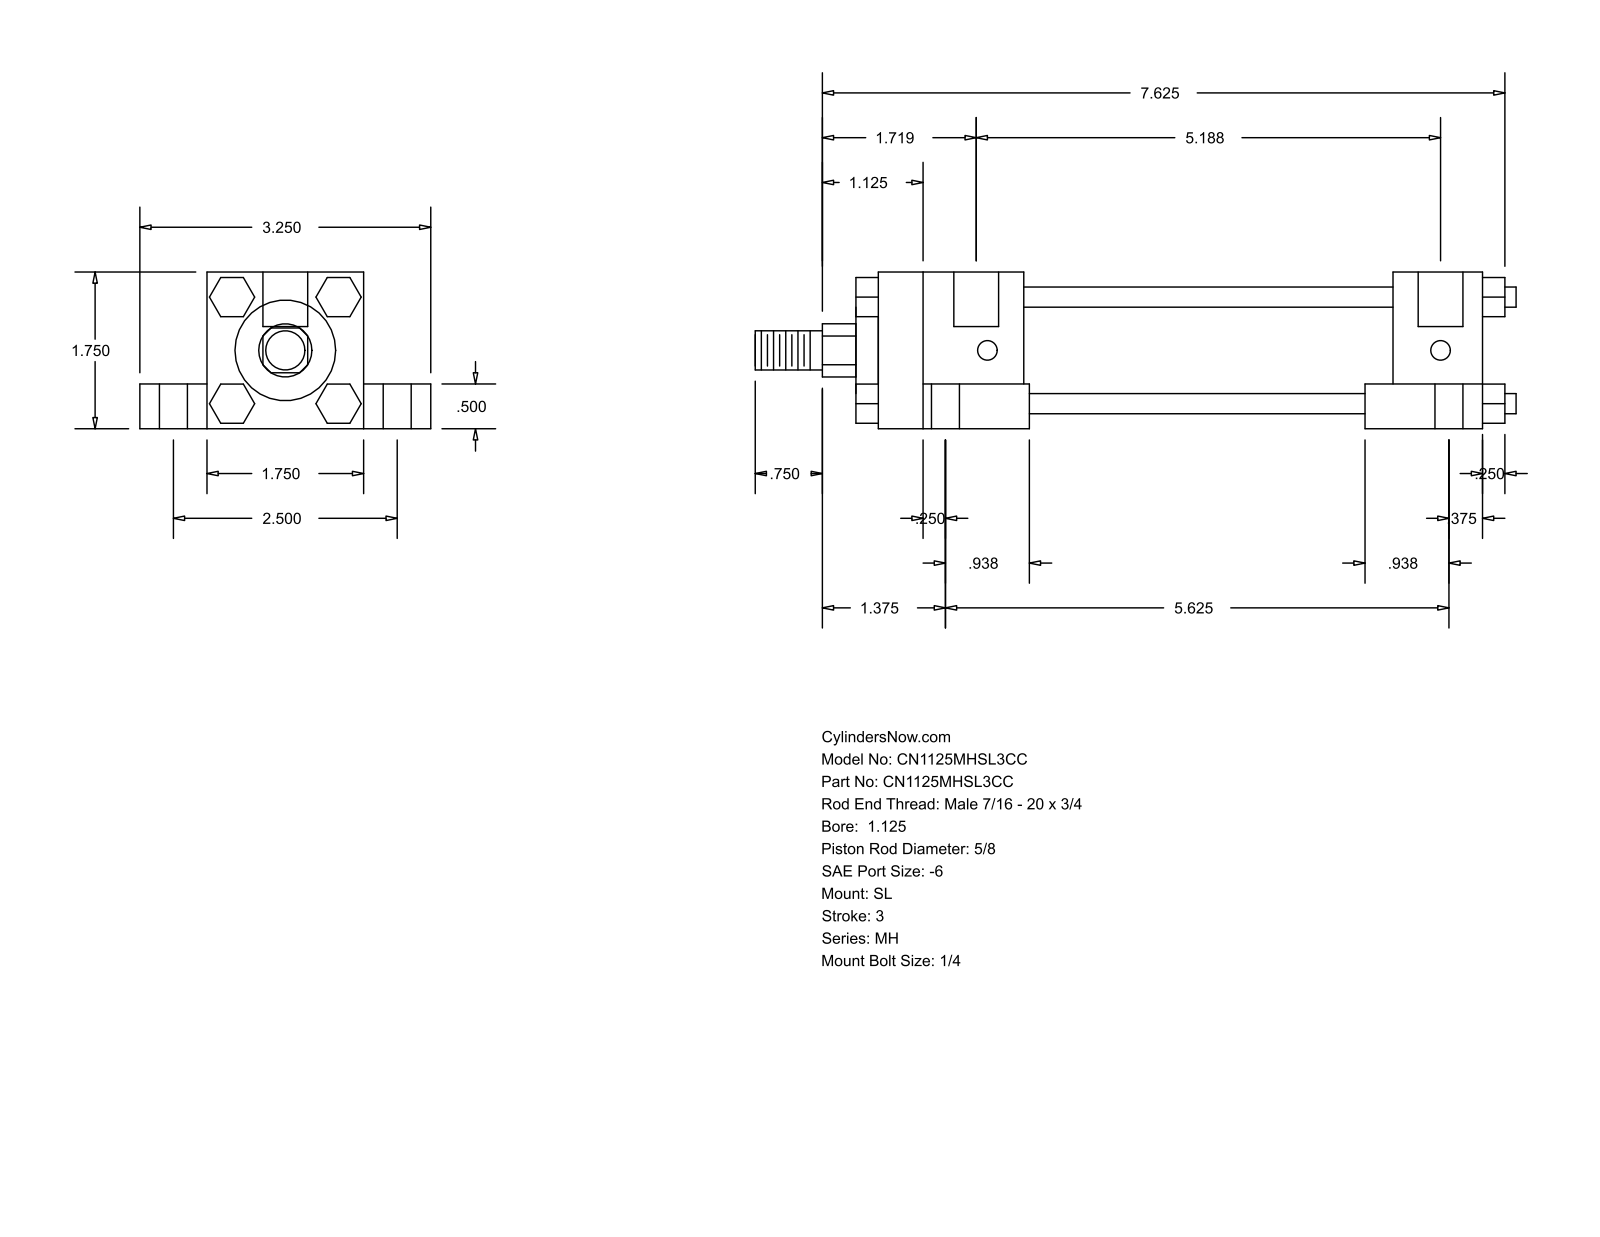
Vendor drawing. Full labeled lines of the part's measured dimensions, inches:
Part name (STEP PRODUCT): MH_SL__0112_0.625
STEP written by: GSSL Pune (CONFIG_CONTROL_DESIGN)
Units: inches
Bodies: 0 solids, 150 faces (114 planar, 36 cylindrical, 0 other)
Overall size (bounding box): 8.5 × 3.25 × 1.75
Round holes (diameter × count): ⌀0.219 ×4, ⌀0.313 ×4, ⌀0.563 ×4, ⌀0.5 ×2
Round bosses / shafts (diameter × count): ⌀0.225 ×4, ⌀1.375 ×1, ⌀1.125 ×1, ⌀0.625 ×1, ⌀0.437 ×1
Partial cylindrical surfaces — rounded edges, fillets, slot ends (radius × count): R0.297 ×1
Main face-to-face distances: 1.75, 0.75, 0.5, 1.25, 2.5, 0.437, 1.875, 4.125, 5.125, 1
Hole centre spacings: 1.254, 1.269, 1.296, 2.5, 5.063, 5.306, 5.427, 5.5
